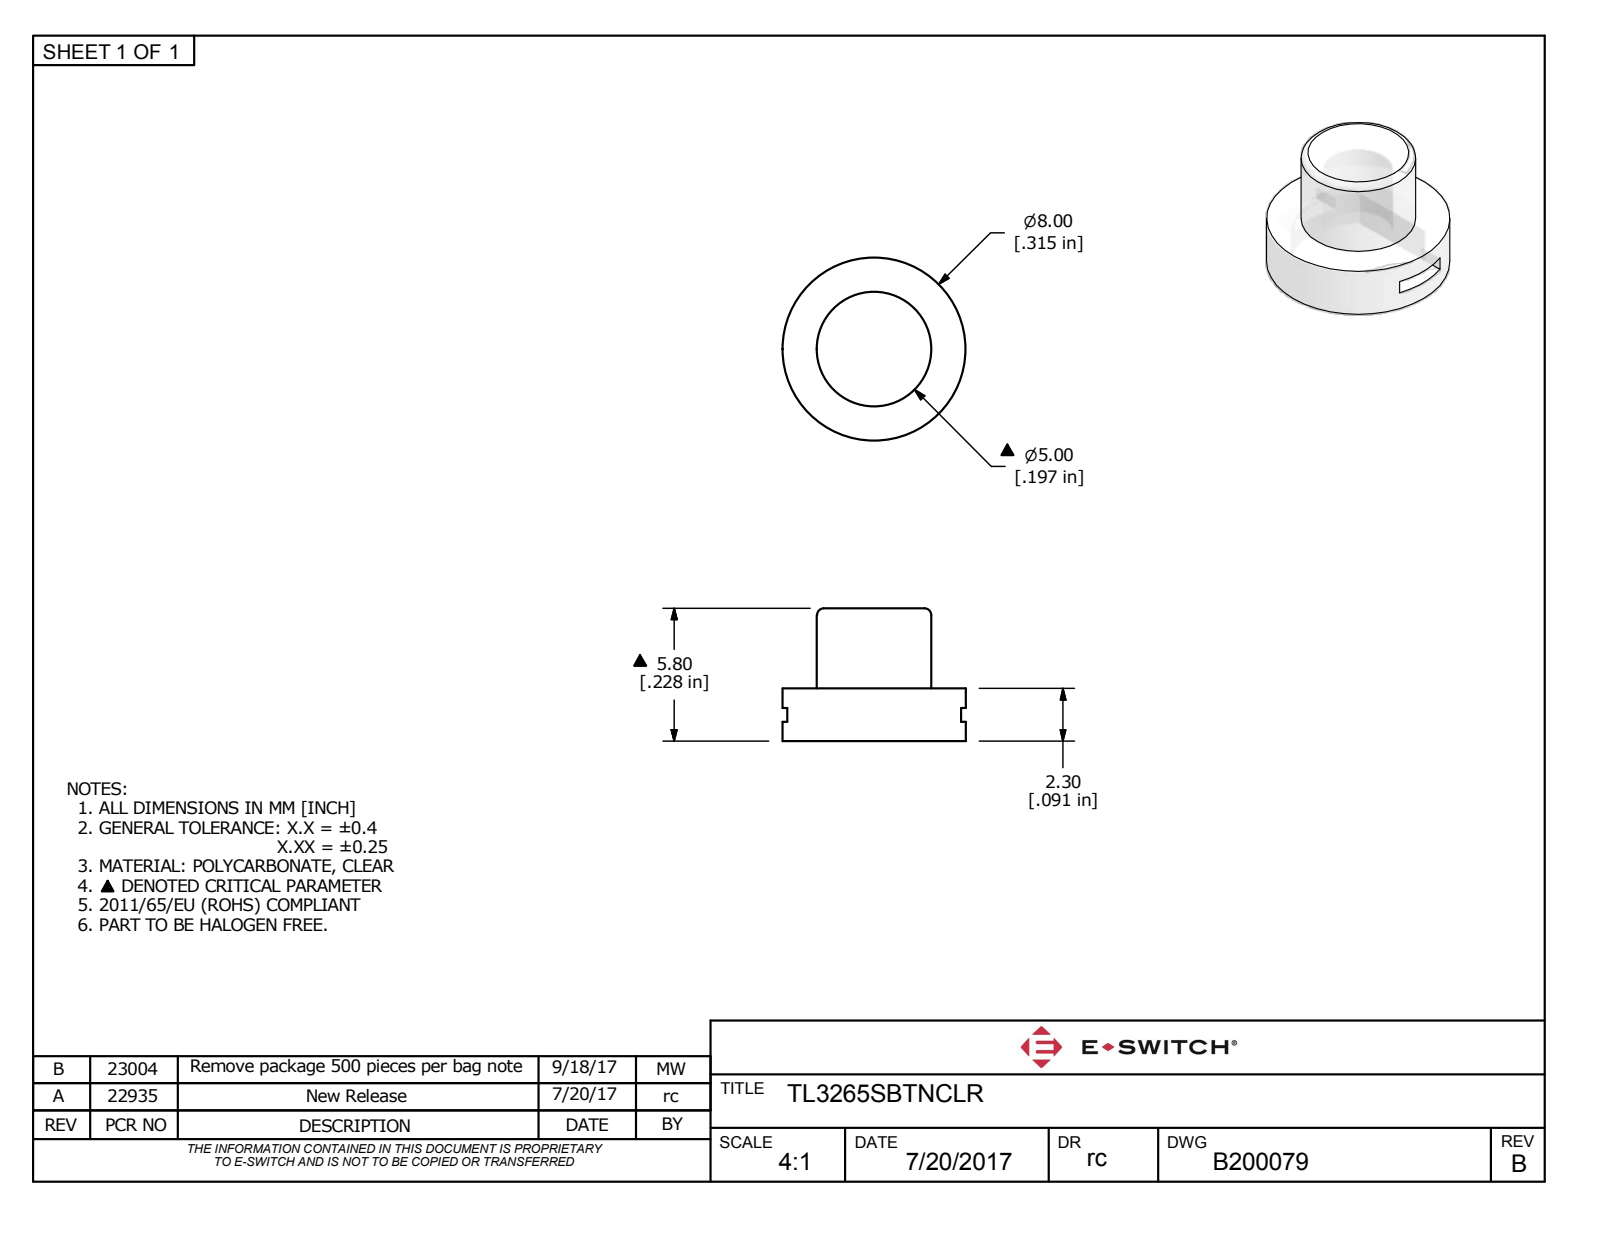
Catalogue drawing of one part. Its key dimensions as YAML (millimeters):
part_name: "TL3265SBTNCLR"
step_written_by: "Autodesk Inventor 2022 (AUTOMOTIVE_DESIGN)"
units: millimeters
bodies: {solids: 1, faces: 21, planar: 15, cylindrical: 5, other: 1}
overall_size: [8, 8, 5.8]
volume: 122
surface_area: 278
round_holes:
  - {diameter: 3, count: 1}
round_bosses_or_shafts:
  - {diameter: 8, count: 1}
  - {diameter: 5, count: 1}
partial_cylinders:
  - {radius: 2.9, count: 1}
face_to_face_distances: [2.3, 4.2, 5.8, 3.5, 1.6, 0.7, 0.85, 1.45, 4.9, 3.3]
